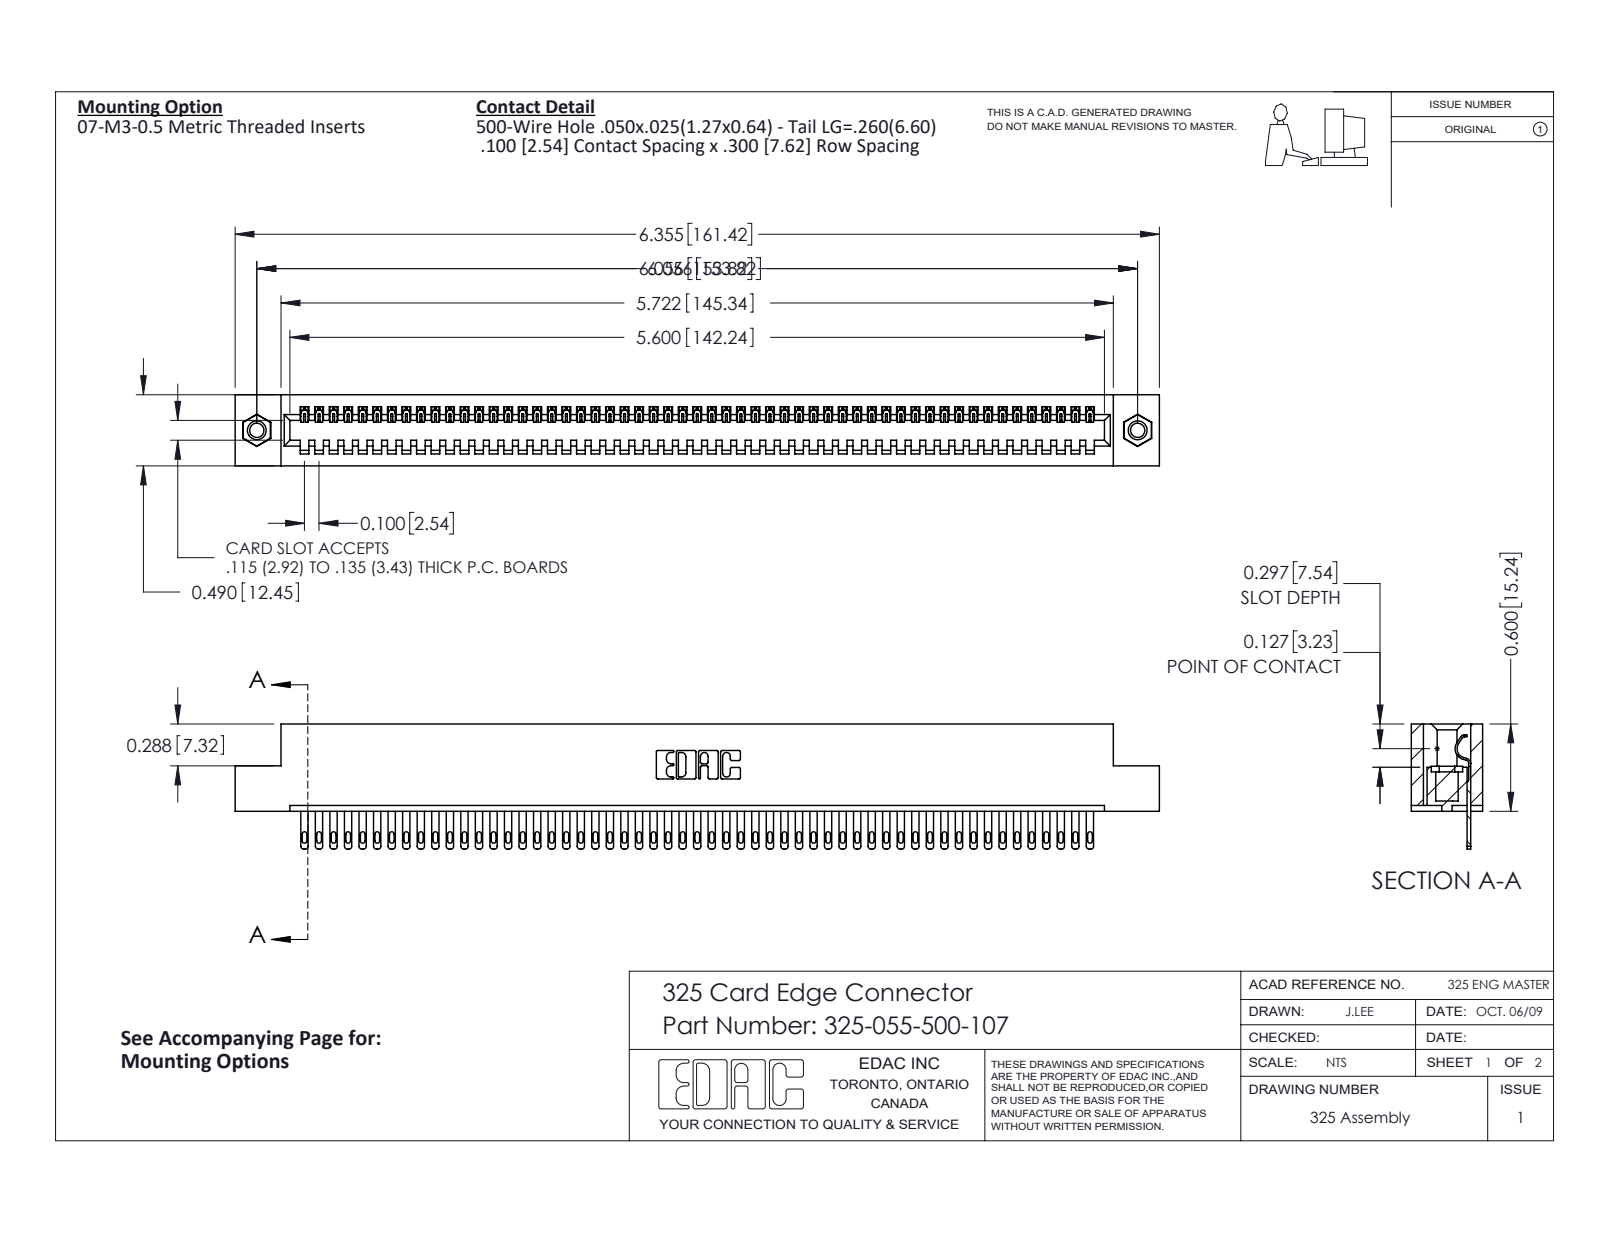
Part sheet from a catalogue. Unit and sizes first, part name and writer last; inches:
Units: inches
Overall size (bounding box): 6.355 × 0.86 × 0.49
Round holes (diameter × count): ⌀0.098 ×2, ⌀0.125 ×2, ⌀0.16 ×2
Round bosses / shafts (diameter × count): ⌀0.155 ×2
Partial cylindrical surfaces — rounded edges, fillets, slot ends (radius × count): R0.006 ×110, R0.016 ×110, R0.02 ×110, R0.01 ×22, R0.007 ×6, R0.031 ×6, R0.026 ×3, R0.014 ×1
Main face-to-face distances: 0.083, 0.407, 0.49, 0.3, 0.107, 0.383, 0.025, 0.325, 0.263, 0.56
Hole centre spacings: 6.056
Volume: 1.258 in³ · Surface area: 35.49 in²
Bodies: 58 solids, 3144 faces (2082 planar, 1046 cylindrical, 16 other)
Part name (STEP PRODUCT): 325-055-500-107; 345-250-001_345-250-005-103; 325-292-001_325-293-100; 325 Part_TI
STEP written by: SolidWorks 2016 (CONFIG_CONTROL_DESIGN)
